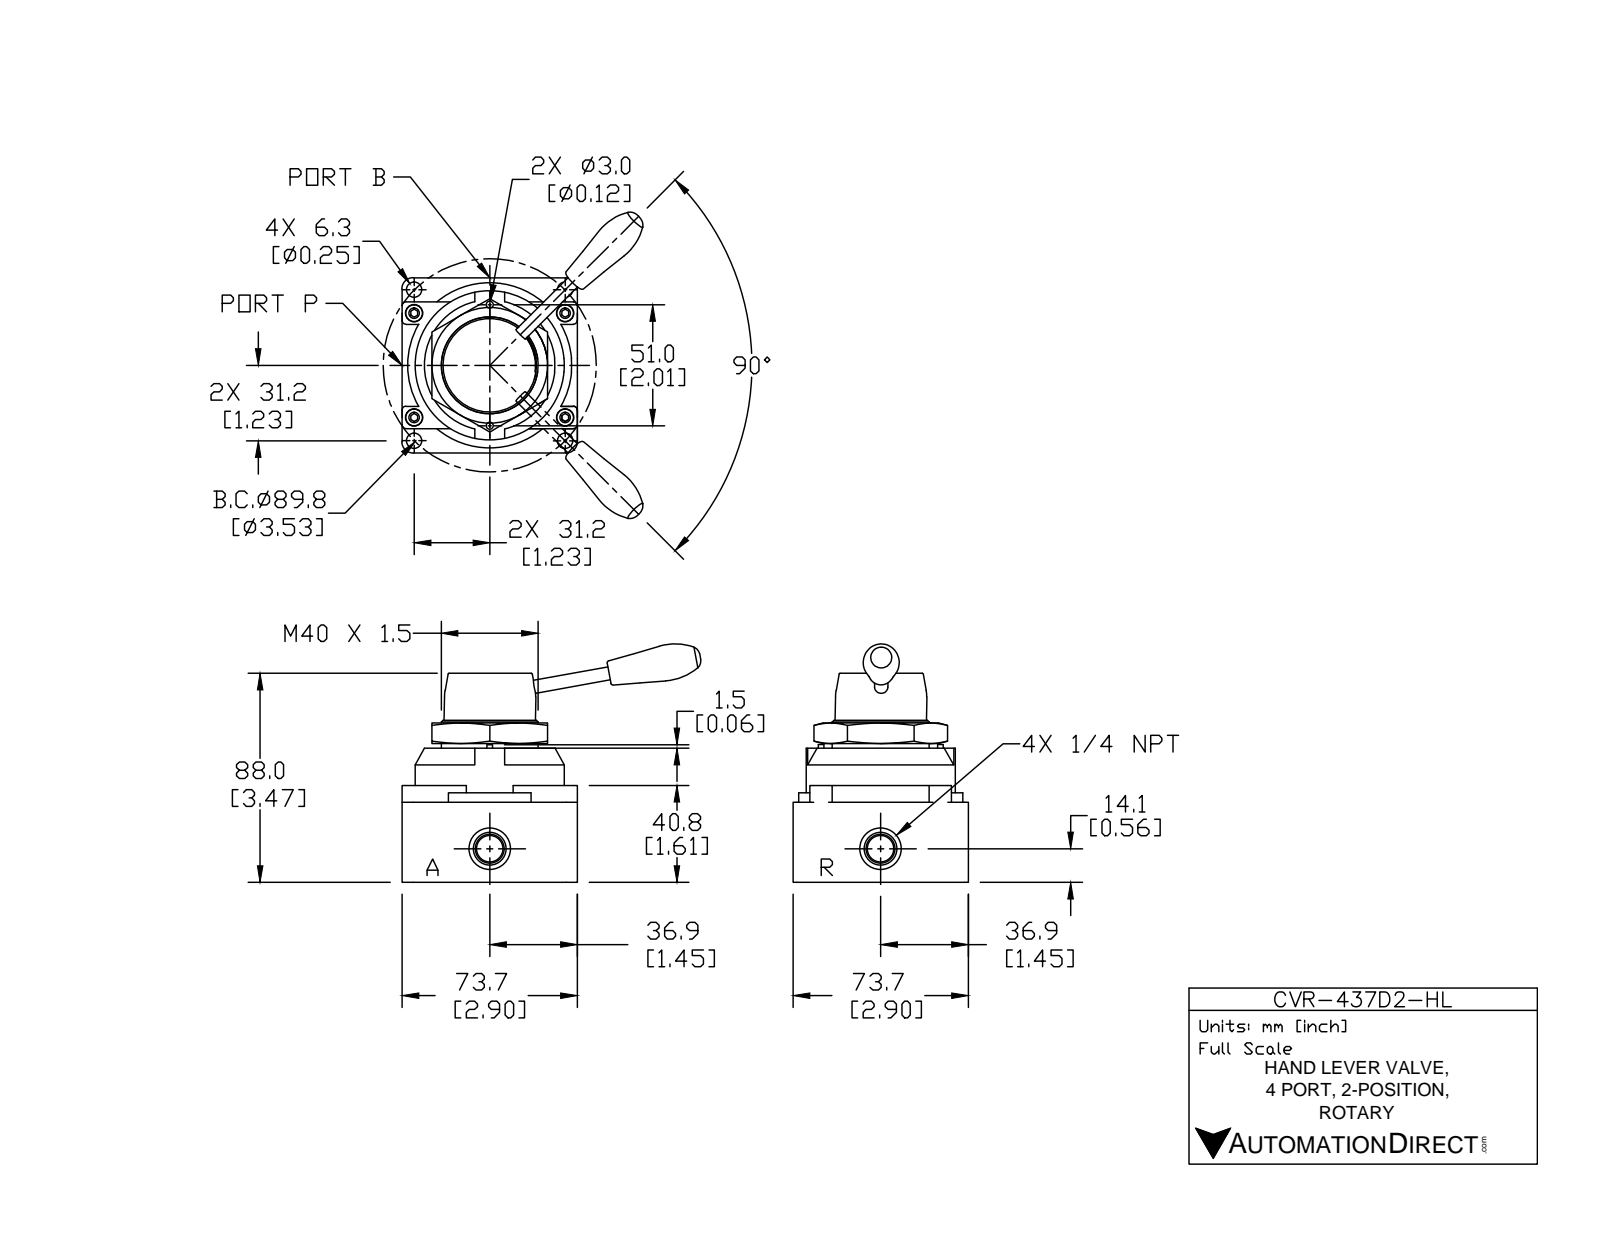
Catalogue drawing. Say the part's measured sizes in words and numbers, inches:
The part is named "CVR-437D2-HL". Its 3-D file was written by "SolidWorks 2015 (CONFIG_CONTROL_DESIGN)". It is 3 solids with 221 faces: 86 planar, 71 cylindrical and 64 other. Overall it measures 5.512 by 4.094 by 2.913 inches. Its volume is 16.8 cubic inches and its surface area 77.85 square inches. Round holes: 4 of diameter 0.26, 4 of diameter 0.362, 2 of diameter 0.702, 1 of diameter 0.787, 1 of diameter 1.299. Round bosses or shafts: 4 of diameter 0.354, 2 of diameter 0.118, 1 of diameter 2.283, 1 of diameter 1.575, 1 of diameter 1.358, 1 of diameter 0.787, 1 of diameter 0.28. Partial cylindrical surfaces (rounded edges, fillets, slot ends): 8 of radius 0.079, 4 of radius 0.039, 4 of radius 0.236, 1 of radius 1.299. The main face-to-face distances are 2.913, 2.795, 1.063, 1.732, 0.472, 0.689, 2.067, 0.512, 1.417, 0.728. The hole center spacings are 2.441, 0.512, 1.411, 1.726, 1.929, 2.494, 3.111, 1.417.
